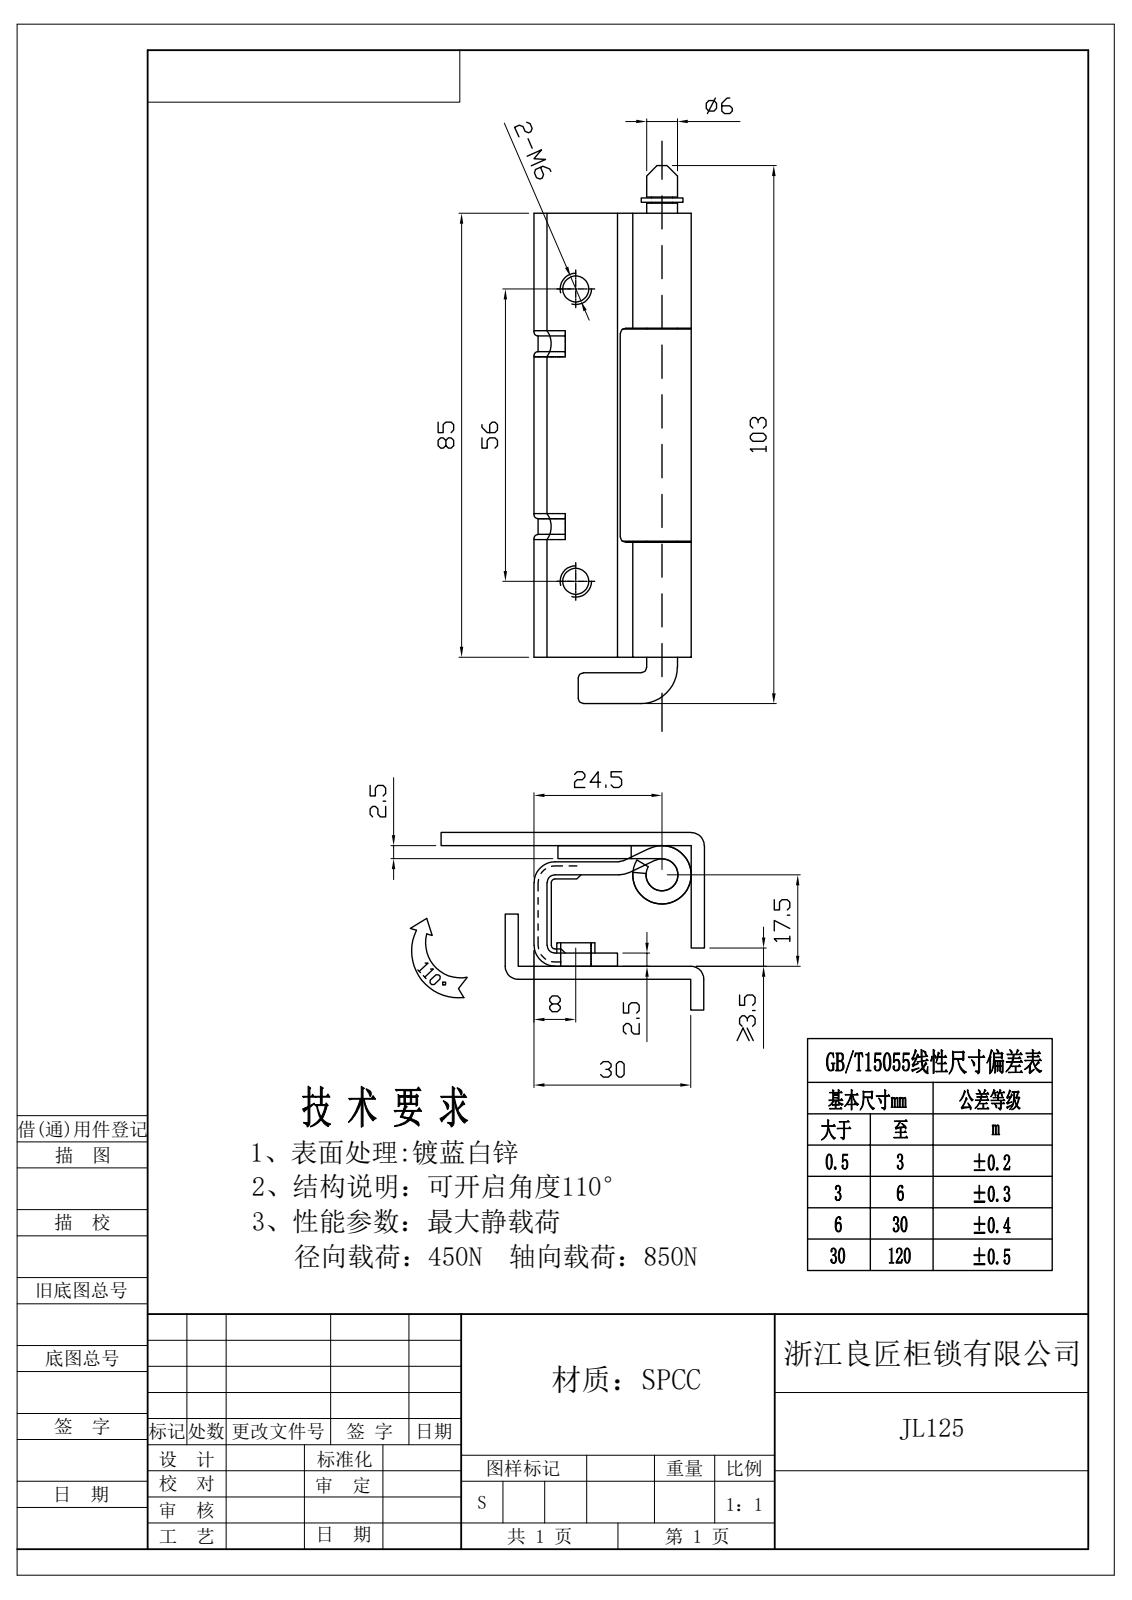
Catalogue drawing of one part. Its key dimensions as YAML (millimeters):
step_written_by: "Rhino 8.5 (CONFIG_CONTROL_DESIGN)"
units: millimeters
bodies: {solids: 3, faces: 170, planar: 42, cylindrical: 72, other: 56}
overall_size: [103.1, 30.1, 23.1]
volume: 21790
surface_area: 19132
round_holes:
  - {diameter: 6, count: 2}
  - {diameter: 3, count: 1}
  - {diameter: 6.2, count: 1}
round_bosses_or_shafts:
  - {diameter: 6, count: 2}
  - {diameter: 11.2, count: 1}
  - {diameter: 8, count: 1}
  - {diameter: 4, count: 1}
partial_cylinders:
  - {radius: 0.5, count: 12}
  - {radius: 2, count: 9}
  - {radius: 1.5, count: 2}
  - {radius: 4, count: 2}
  - {radius: 4.5, count: 1}
face_to_face_distances: [2.5, 3.1, 17.5, 20.6, 5.6, 0.6, 15, 18.1, 20, 23.1]
hole_center_spacings: [28.55, 56]
